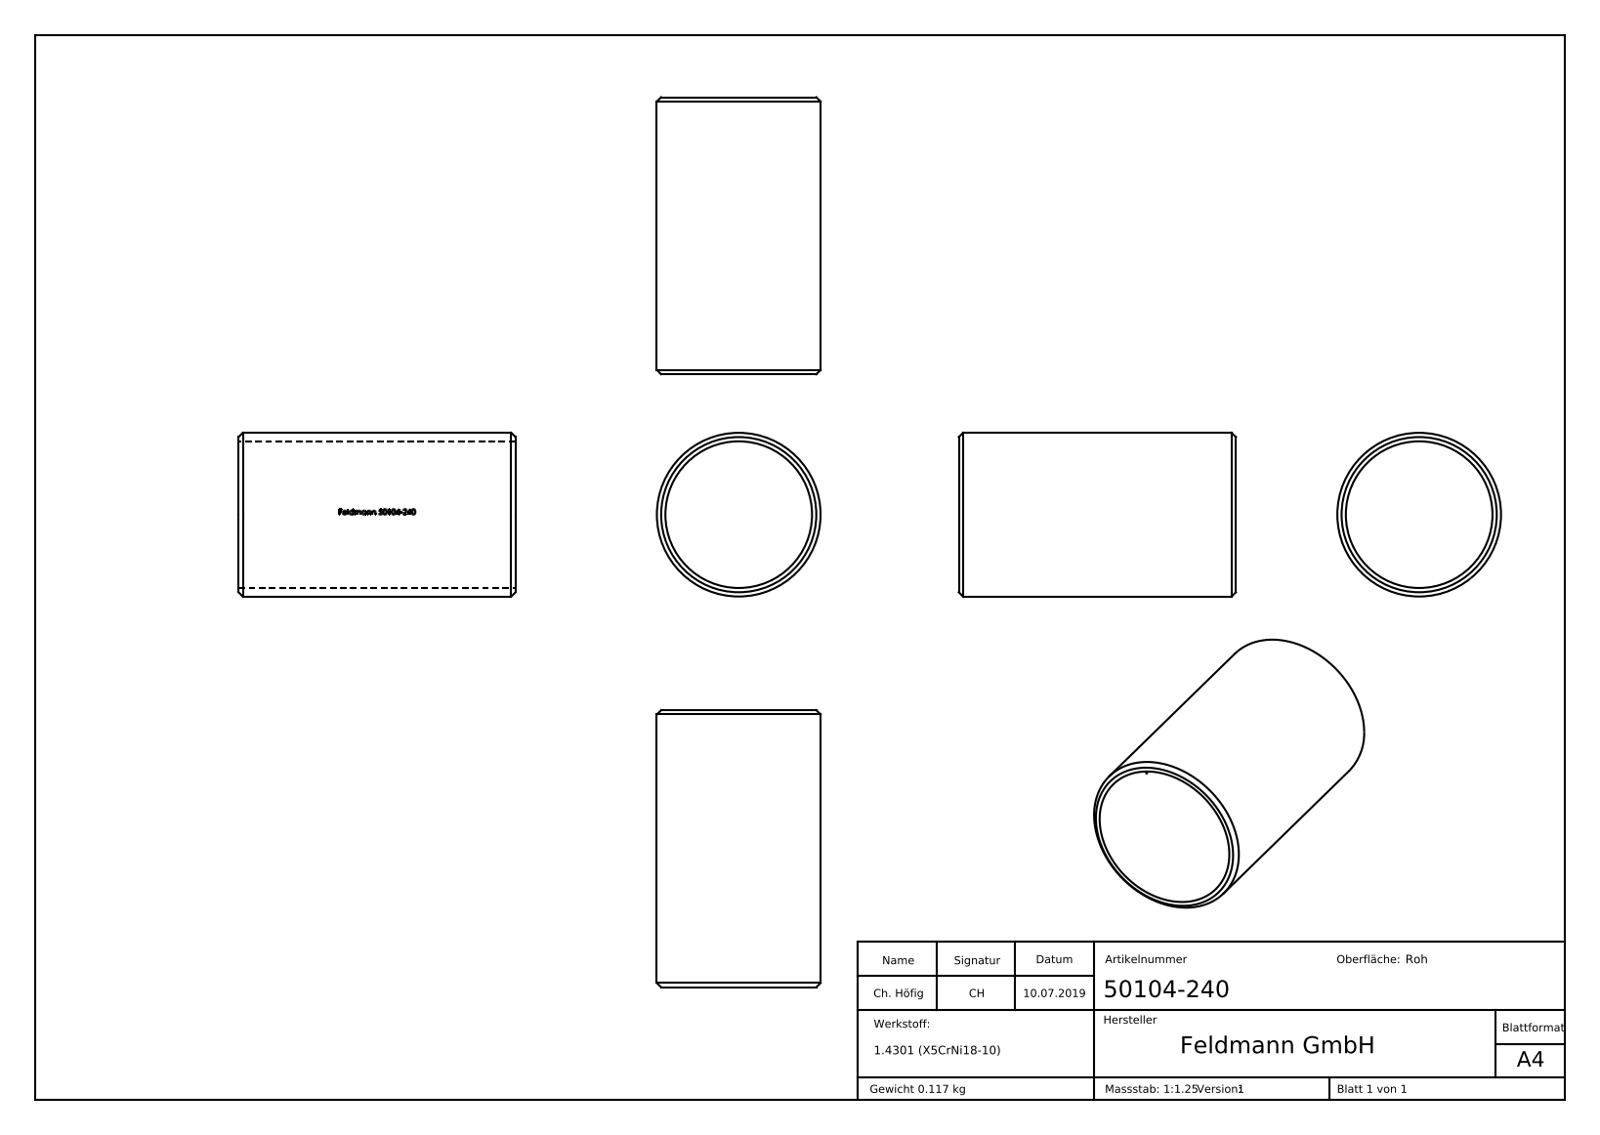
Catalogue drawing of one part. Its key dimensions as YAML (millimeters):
part_name: "50104-240"
step_written_by: "SolidWorks 2015 (CONFIG_CONTROL_DESIGN)"
units: millimeters
bodies: {solids: 1, faces: 239, planar: 104, cylindrical: 42, other: 93}
overall_size: [65, 38.4, 38.4]
volume: 14747
surface_area: 15189
round_holes:
  - {diameter: 34.4, count: 1}
round_bosses_or_shafts:
  - {diameter: 38.4, count: 1}
partial_cylinders:
  - {radius: 17.3, count: 1}
face_to_face_distances: [65, 0.88, 0.44, 11.73, 14.62, 2.26, 0.39, 8.46, 2.18, 10.72]
